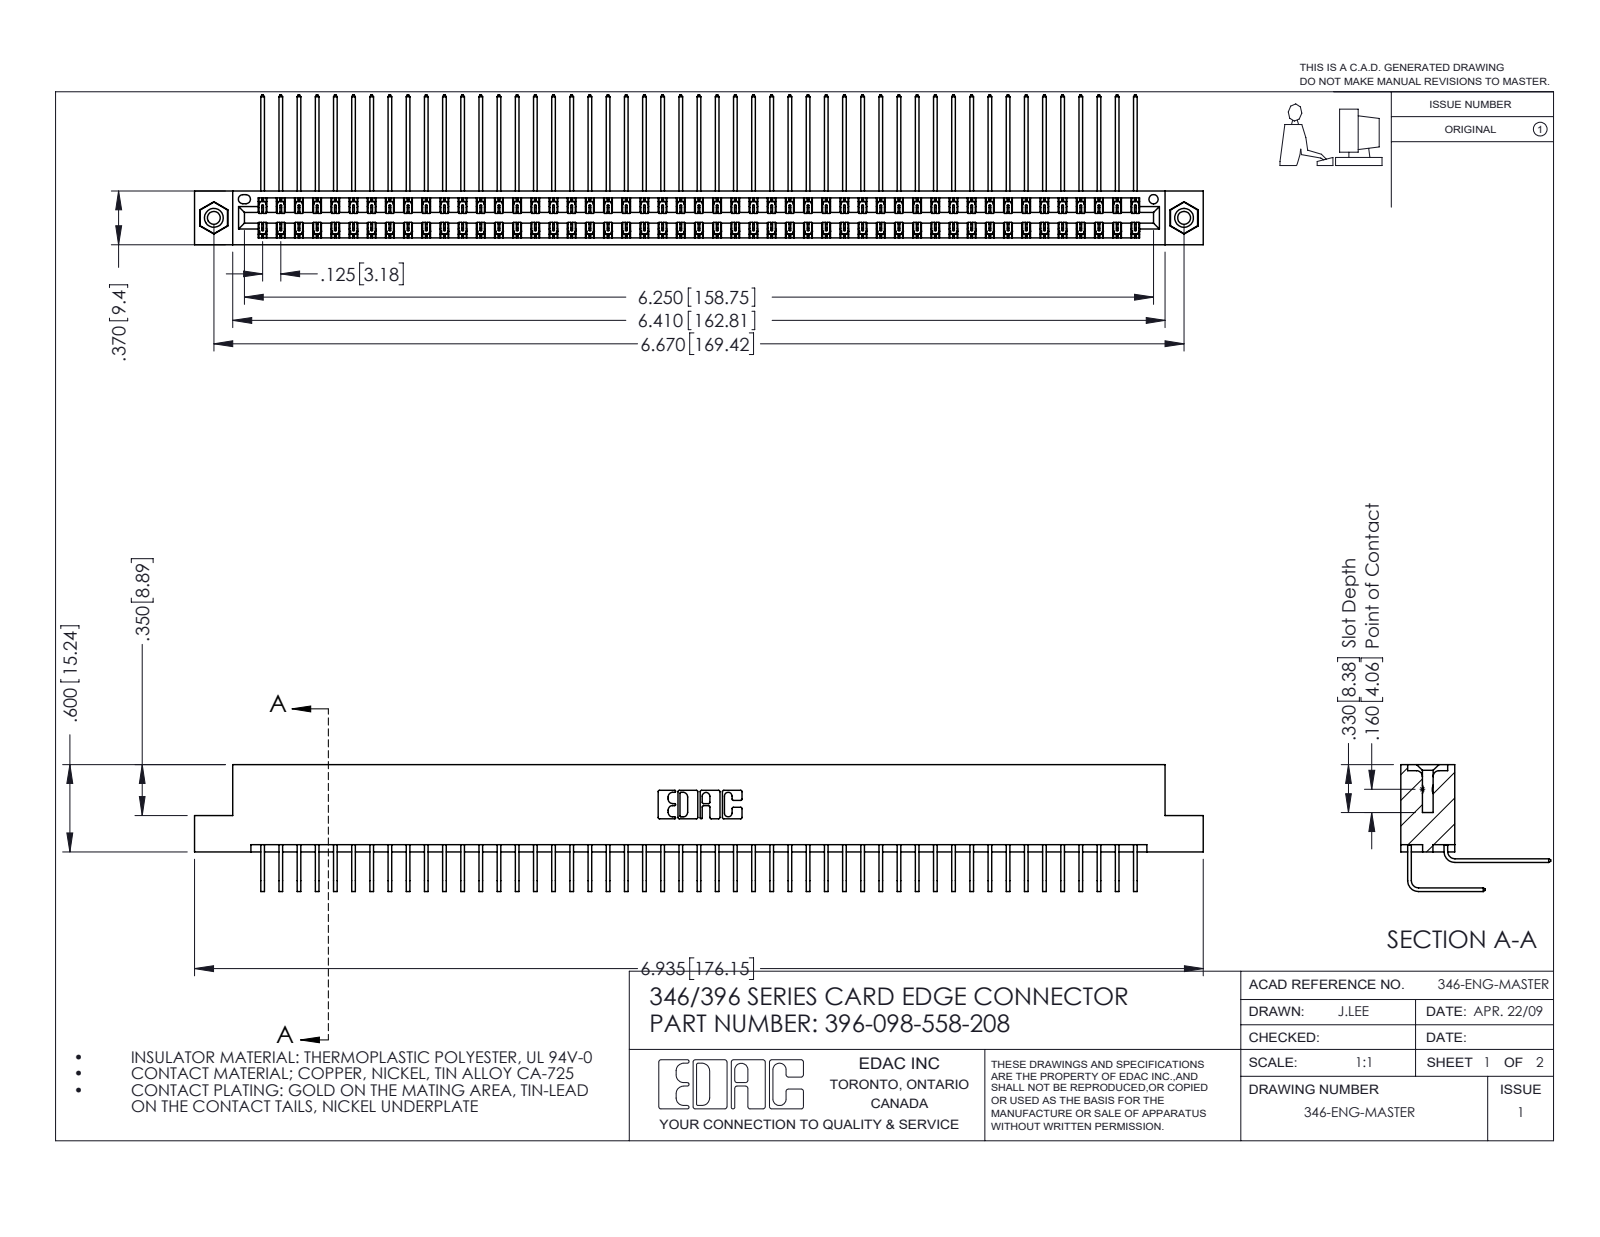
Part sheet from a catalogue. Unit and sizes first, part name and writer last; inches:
Units: inches
Overall size (bounding box): 6.935 × 1.03 × 0.873
Round holes (diameter × count): ⌀0.089 ×2, ⌀0.125 ×2, ⌀0.156 ×2, ⌀0.064 ×1
Round bosses / shafts (diameter × count): ⌀0.155 ×2
Partial cylindrical surfaces — rounded edges, fillets, slot ends (radius × count): R0.006 ×147, R0.01 ×22, R0.007 ×6, R0.031 ×6, R0.026 ×3, R0.014 ×2, R0.022 ×2, R0.024 ×2
Main face-to-face distances: 0.048, 0.322, 0.025, 0.37, 0.25, 0.072, 0.298, 0.275, 0.148, 0.222
Hole centre spacings: 0.246, 6.461, 6.67
Volume: 1.086 in³ · Surface area: 42.31 in²
Bodies: 101 solids, 5474 faces (3734 planar, 1724 cylindrical, 16 other)
Part name (STEP PRODUCT): 346 Part_Flush Mounting Lugs - 0.156 Dia-TI; 345-292-001_558 559 Tail - 1; 396-098-558-208; 345-292-001_558 Tail - 2 (+1 more)
STEP written by: SolidWorks 2016 (CONFIG_CONTROL_DESIGN)
